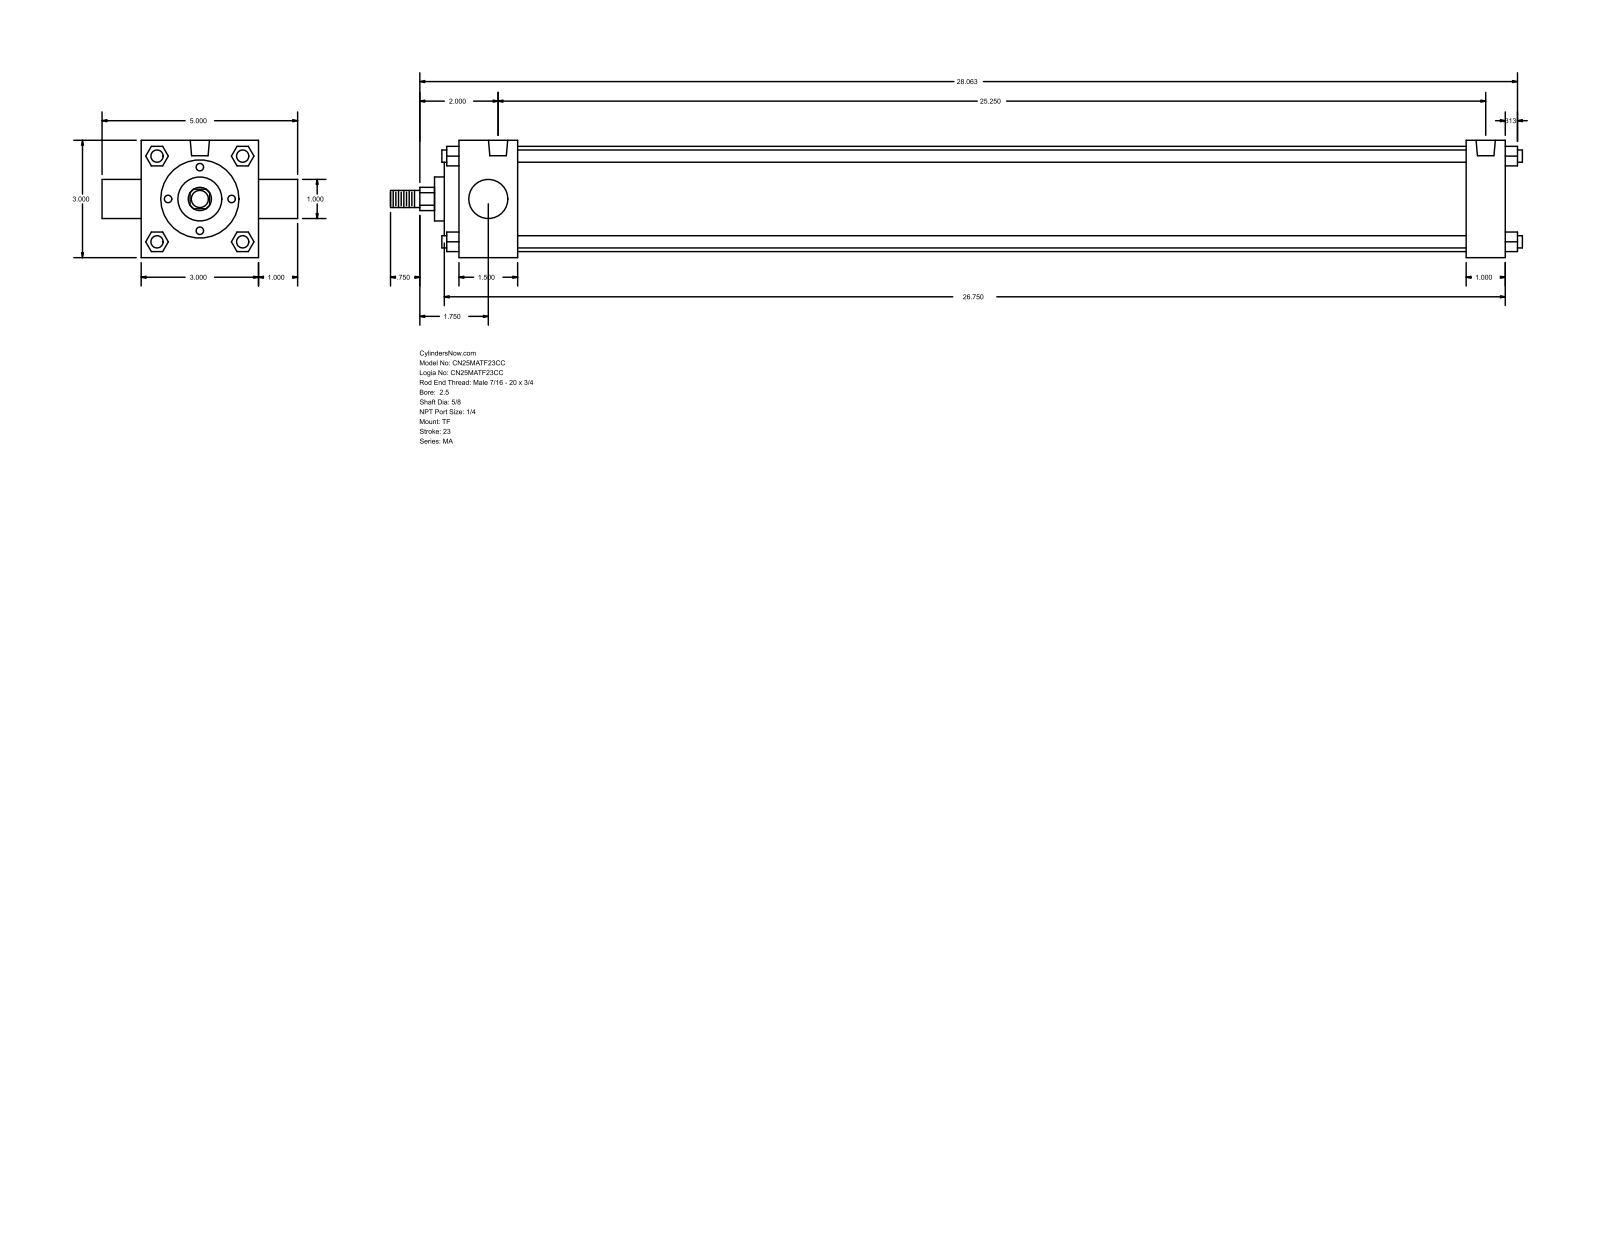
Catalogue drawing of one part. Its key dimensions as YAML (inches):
part_name: "MA_TF__0250_0.625"
step_written_by: "GSSL Pune (CONFIG_CONTROL_DESIGN)"
units: inches
bodies: {solids: 0, faces: 122, planar: 93, cylindrical: 29, other: 0}
overall_size: [28.937, 5, 3]
round_holes:
  - {diameter: 0.313, count: 3}
  - {diameter: 0.492, count: 2}
round_bosses_or_shafts:
  - {diameter: 0.313, count: 4}
  - {diameter: 2.69, count: 1}
  - {diameter: 2, count: 1}
  - {diameter: 1.125, count: 1}
  - {diameter: 1, count: 1}
  - {diameter: 0.625, count: 1}
  - {diameter: 0.437, count: 1}
partial_cylinders:
  - {radius: 0.297, count: 1}
face_to_face_distances: [3, 26.75, 1, 1.5, 25.75, 24.25, 25.25, 0.5, 0.375, 1.875]
hole_center_spacings: [25.25]
